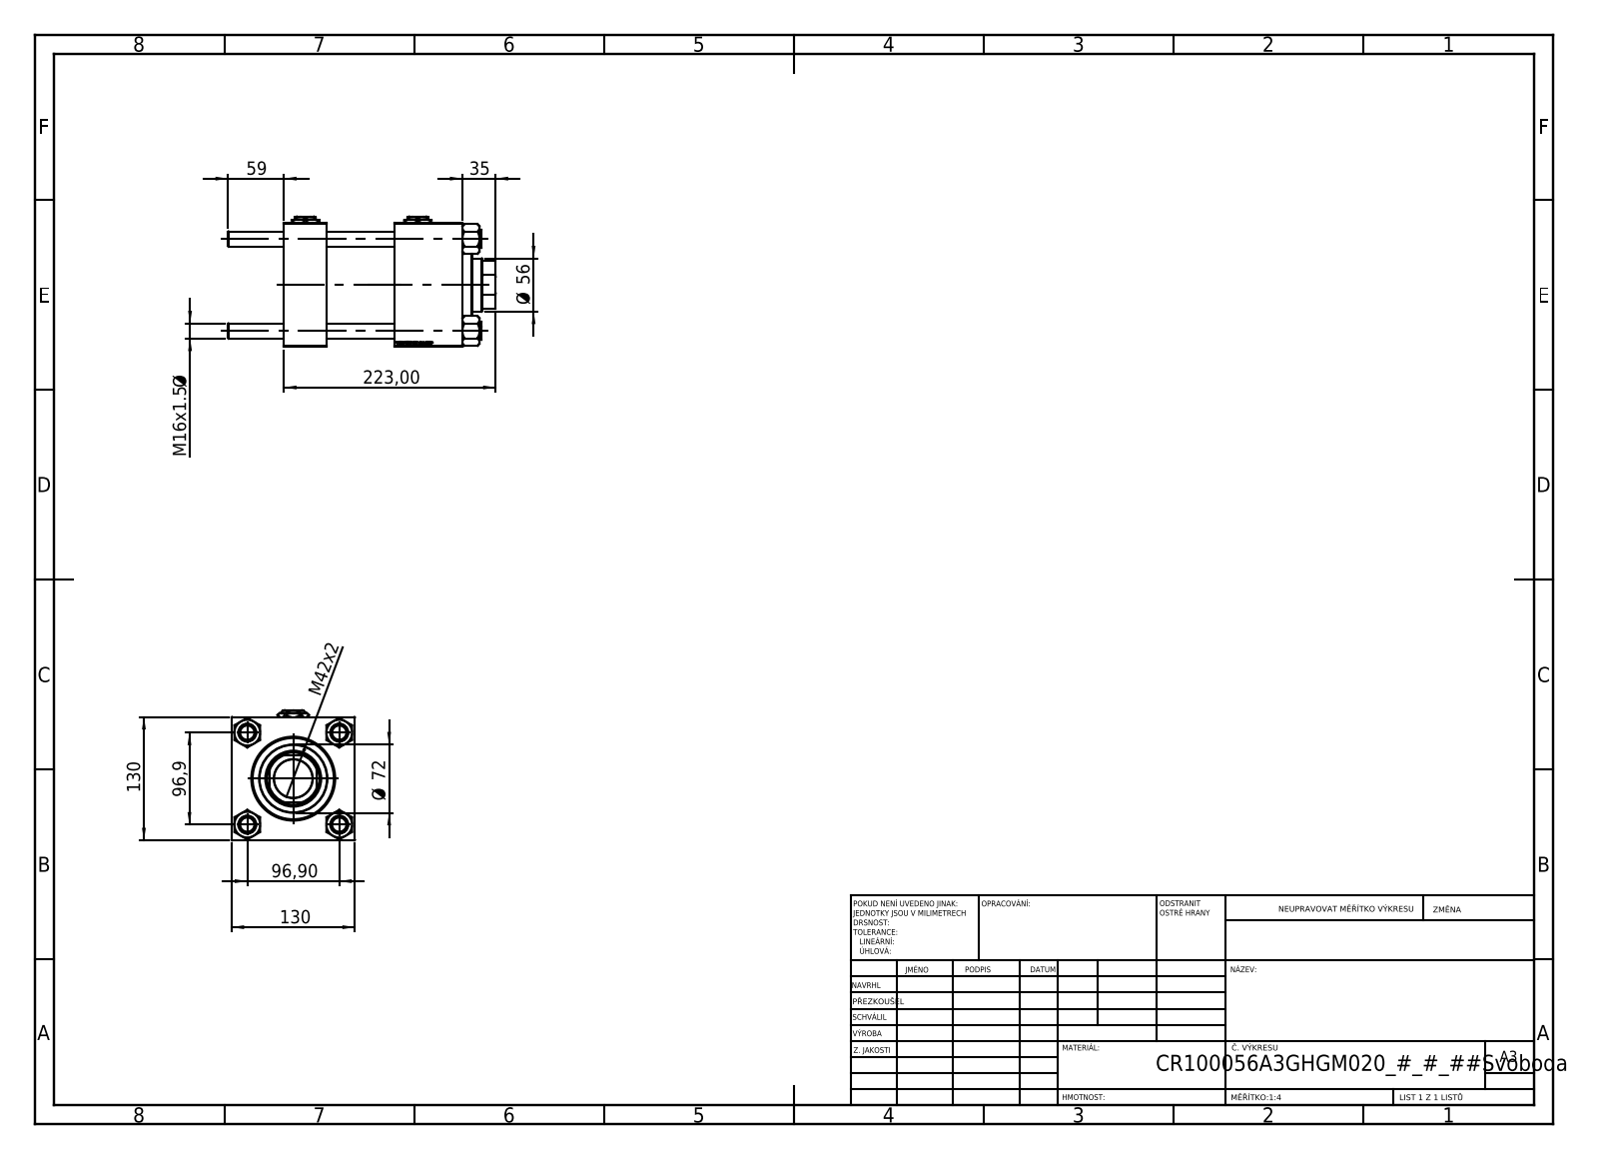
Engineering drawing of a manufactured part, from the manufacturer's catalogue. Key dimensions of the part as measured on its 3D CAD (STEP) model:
Part name (STEP PRODUCT): Zatka_pro_OIL_PORT; NUT_M5; V215CR_BODY_A; V215CR_VCP (+2 more)
STEP written by: SolidWorks 2019 (CONFIG_CONTROL_DESIGN)
Units: millimetres
Bodies: 13 solids, 1281 faces (615 planar, 88 cylindrical, 578 other)
Overall size (bounding box): 282 × 137 × 130
Volume: 2 540 000 mm³ · Surface area: 367 655 mm²
Round holes (diameter × count): ⌀16 ×4, ⌀7 ×2, ⌀26.44 ×2, ⌀35 ×2, ⌀40.5 ×1, ⌀56 ×1, ⌀59 ×1, ⌀76 ×1, ⌀85.5 ×1, ⌀100 ×1
Round bosses / shafts (diameter × count): ⌀19 ×4, ⌀106 ×1, ⌀72 ×1
Partial cylindrical surfaces — rounded edges, fillets, slot ends (radius × count): R27 ×1
Main face-to-face distances: 130, 45, 188, 143, 71, 116, 72, 20, 92, 96
Hole centre spacings: 68.52, 96.9, 137.04, 118.5
